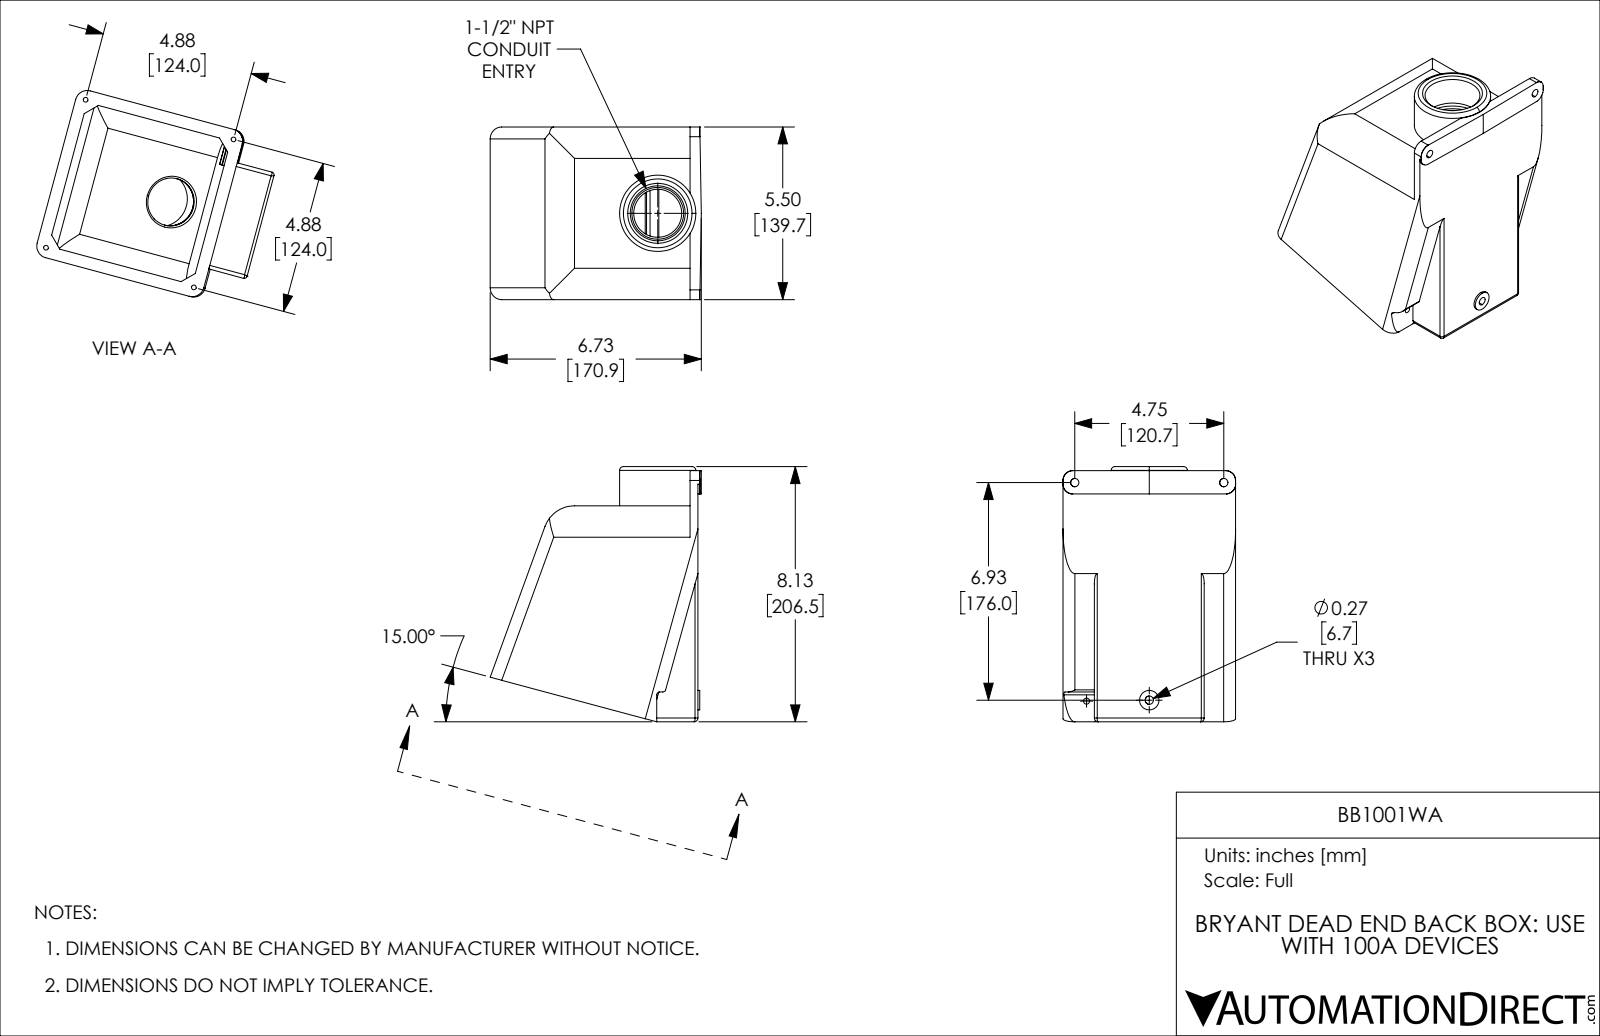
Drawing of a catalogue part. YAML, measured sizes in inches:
part_name: "BB1001WA"
step_written_by: "SolidWorks 2021 (CONFIG_CONTROL_DESIGN)"
units: inches
bodies: {solids: 4, faces: 534, planar: 246, cylindrical: 133, other: 155}
overall_size: [8.13, 6.728, 5.5]
volume: 34.71
surface_area: 353.3
round_holes:
  - {diameter: 0.15, count: 4}
  - {diameter: 0.265, count: 2}
  - {diameter: 0.193, count: 1}
  - {diameter: 0.265, count: 1}
  - {diameter: 0.312, count: 1}
  - {diameter: 0.511, count: 1}
  - {diameter: 0.56, count: 1}
  - {diameter: 1.53, count: 1}
  - {diameter: 1.75, count: 1}
  - {diameter: 1.96, count: 1}
round_bosses_or_shafts:
  - {diameter: 2.43, count: 1}
  - {diameter: 0.626, count: 1}
  - {diameter: 0.62, count: 1}
partial_cylinders:
  - {radius: 0.09, count: 20}
  - {radius: 0.125, count: 4}
  - {radius: 0.31, count: 4}
  - {radius: 0.38, count: 4}
  - {radius: 0.12, count: 3}
  - {radius: 0.81, count: 3}
  - {radius: 1, count: 3}
  - {radius: 0.19, count: 2}
face_to_face_distances: [0.19, 5.31, 5.12, 5.5, 1, 4.31, 0.19, 4.12, 1.19, 0.25]
hole_center_spacings: [4.88, 6.902, 1, 4.75, 7.325, 7.326]
